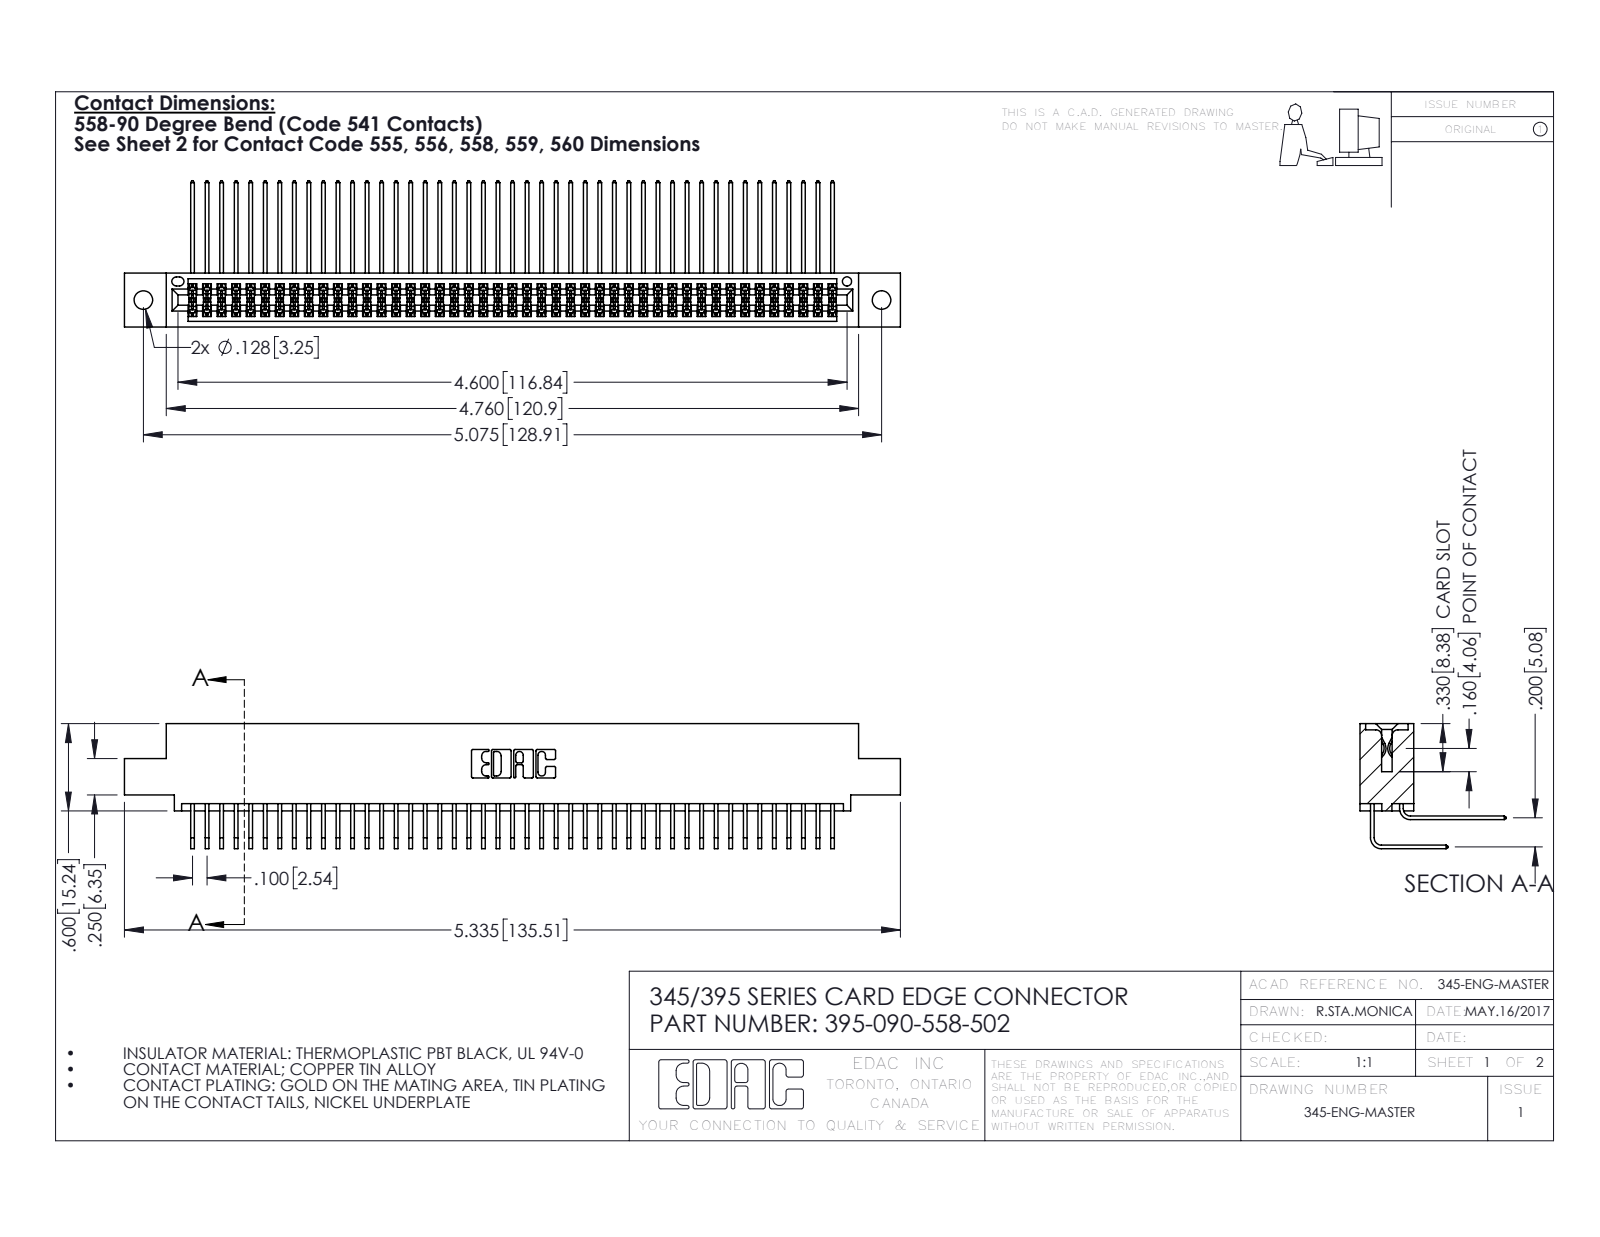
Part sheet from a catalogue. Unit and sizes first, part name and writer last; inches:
Units: inches
Overall size (bounding box): 5.335 × 1.005 × 0.859
Round holes (diameter × count): ⌀0.128 ×2, ⌀0.064 ×1
Partial cylindrical surfaces — rounded edges, fillets, slot ends (radius × count): R0.006 ×136, R0.01 ×22, R0.007 ×6, R0.031 ×6, R0.026 ×3, R0.014 ×2, R0.019 ×2, R0.022 ×2
Main face-to-face distances: 0.072, 0.298, 0.2, 0.37, 0.098, 0.272, 0.025, 0.225, 0.025, 0.175
Hole centre spacings: 0.27, 4.839, 5.075
Volume: 0.83 in³ · Surface area: 34.76 in²
Bodies: 91 solids, 4810 faces (3234 planar, 1576 cylindrical, 0 other)
Part name (STEP PRODUCT): 345-292-001_558 Tail - 2; 345-292-001_558 559 Tail - 1; 395-090-558-502; 345 Part_0.110 Offset - 0.128 Dia
STEP written by: SolidWorks 2016 (CONFIG_CONTROL_DESIGN)
